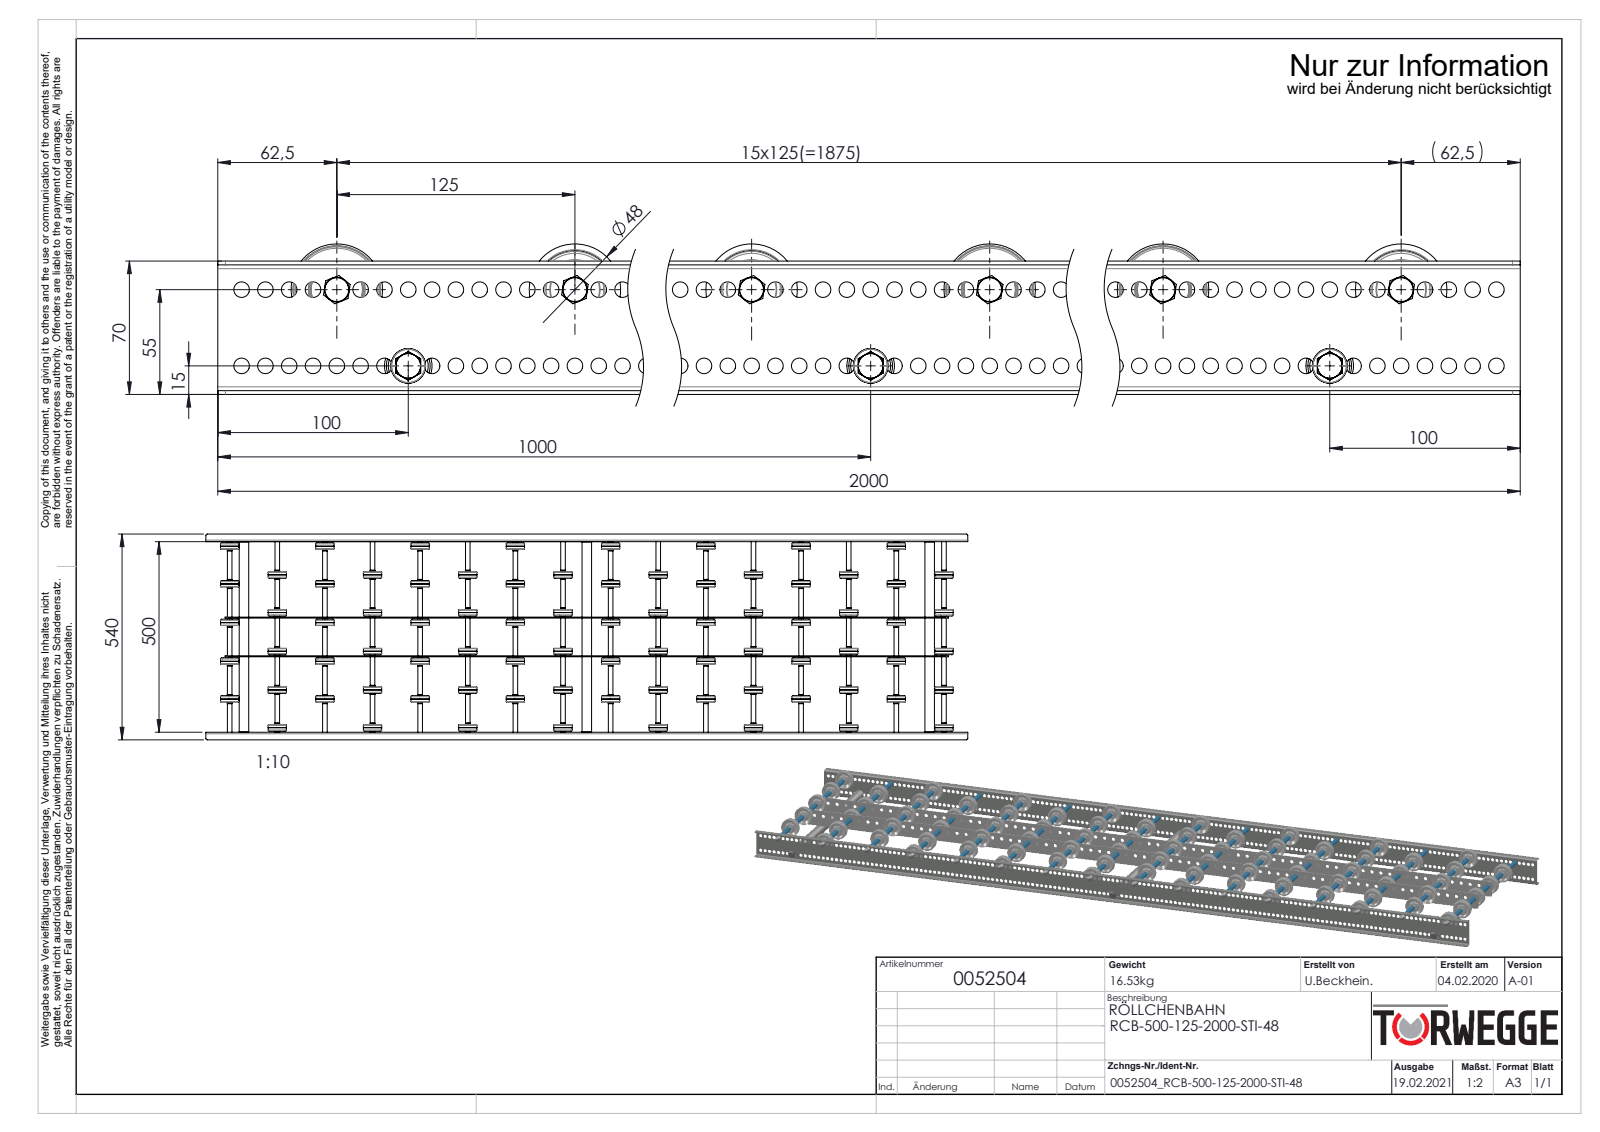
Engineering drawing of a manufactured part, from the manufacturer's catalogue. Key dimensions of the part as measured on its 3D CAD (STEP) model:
Part name (STEP PRODUCT): S100100_Längstraverse-42x2,5_S100149_Lngstraverse-RB-L1899; Hutmutter_DIN_1587_M8; S106837_Gewindestange-M8-KFG_L520; 0052504 (+6 more)
STEP written by: SolidWorks 2020 (AUTOMOTIVE_DESIGN)
Units: millimetres
Bodies: 307 solids, 9894 faces (1902 planar, 4220 cylindrical, 3772 other)
Overall size (bounding box): 2000 × 540 × 79
Volume: 3 763 000 mm³ · Surface area: 3 011 000 mm²
Round holes (diameter × count): ⌀8.2 ×318, ⌀8.5 ×76, ⌀6.65 ×16, ⌀8 ×16, ⌀9.65 ×16, ⌀15 ×16, ⌀41 ×16, ⌀6.8 ×3, ⌀21 ×3
Round bosses / shafts (diameter × count): ⌀48 ×16, ⌀13 ×16, ⌀12.5 ×16, ⌀12.4 ×16, ⌀12 ×16, ⌀11.5 ×16, ⌀25 ×3, ⌀8 ×3
Partial cylindrical surfaces — rounded edges, fillets, slot ends (radius × count): R4 ×8, R2 ×4, R5 ×4
Main face-to-face distances: 2, 101.5, 200.5, 302, 502, 99, 12, 87, 200, 202.5
Hole centre spacings: 12.5, 25, 37.5, 50, 62.5, 75, 87.5, 100
